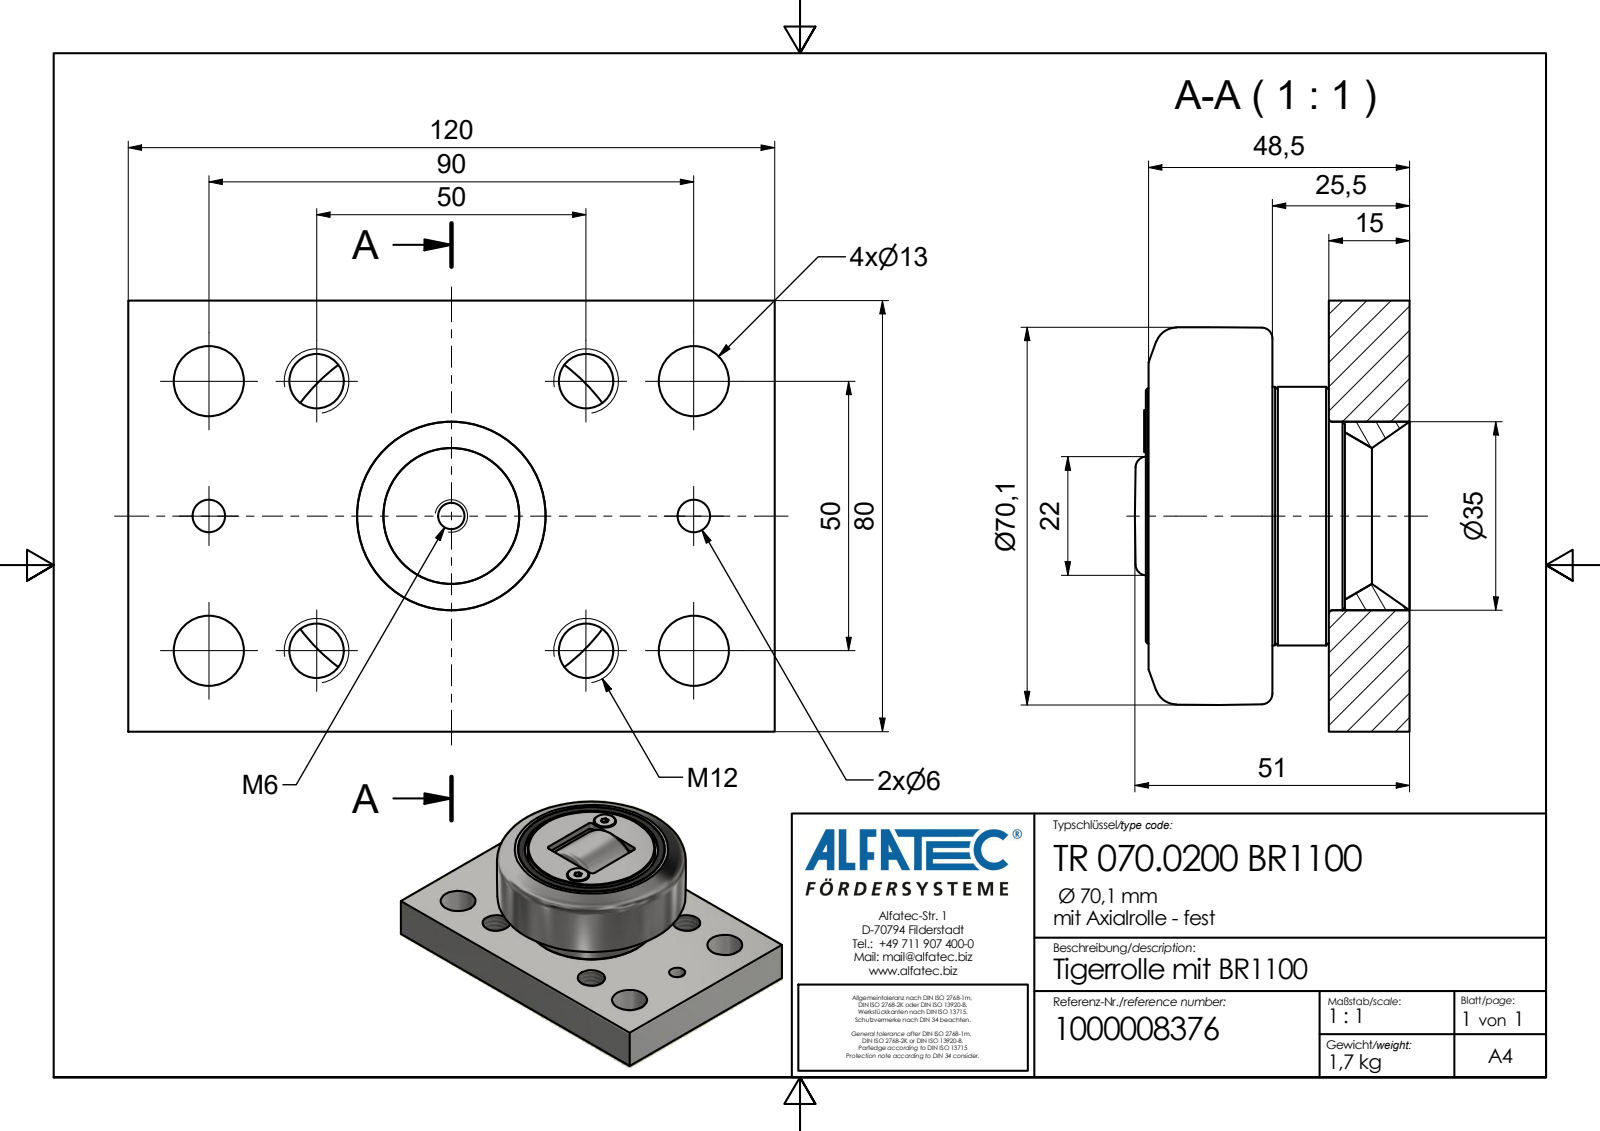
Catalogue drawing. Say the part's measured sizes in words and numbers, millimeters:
The part is named "TR 070.0200 BR1100_Kontur". Its 3-D file was written by "Autodesk Inventor 2020 (AP242_MANAGED_MODEL_BASED_3D_ENGINEERING_MIM_LF)". It is 1 solid with 70 faces: 36 planar, 21 cylindrical and 13 other. Overall it measures 120 by 80 by 51 millimeters. Its volume is 231 746 cubic millimeters and its surface area 39 270 square millimeters. Round holes: 4 of diameter 10.11, 4 of diameter 13, 2 of diameter 6, 1 of diameter 2.5, 1 of diameter 4.92. Round bosses or shafts: 2 of diameter 7.8, 1 of diameter 48, 1 of diameter 47.3. Partial cylindrical surfaces (rounded edges, fillets, slot ends): 4 of radius 1. The main face-to-face distances are 15, 80, 25.5, 10.5, 120, 23.5, 0.5, 49, 34, 23. The hole center spacings are 50, 20, 25, 32.02, 35.36, 51.48, 53.85, 70.
